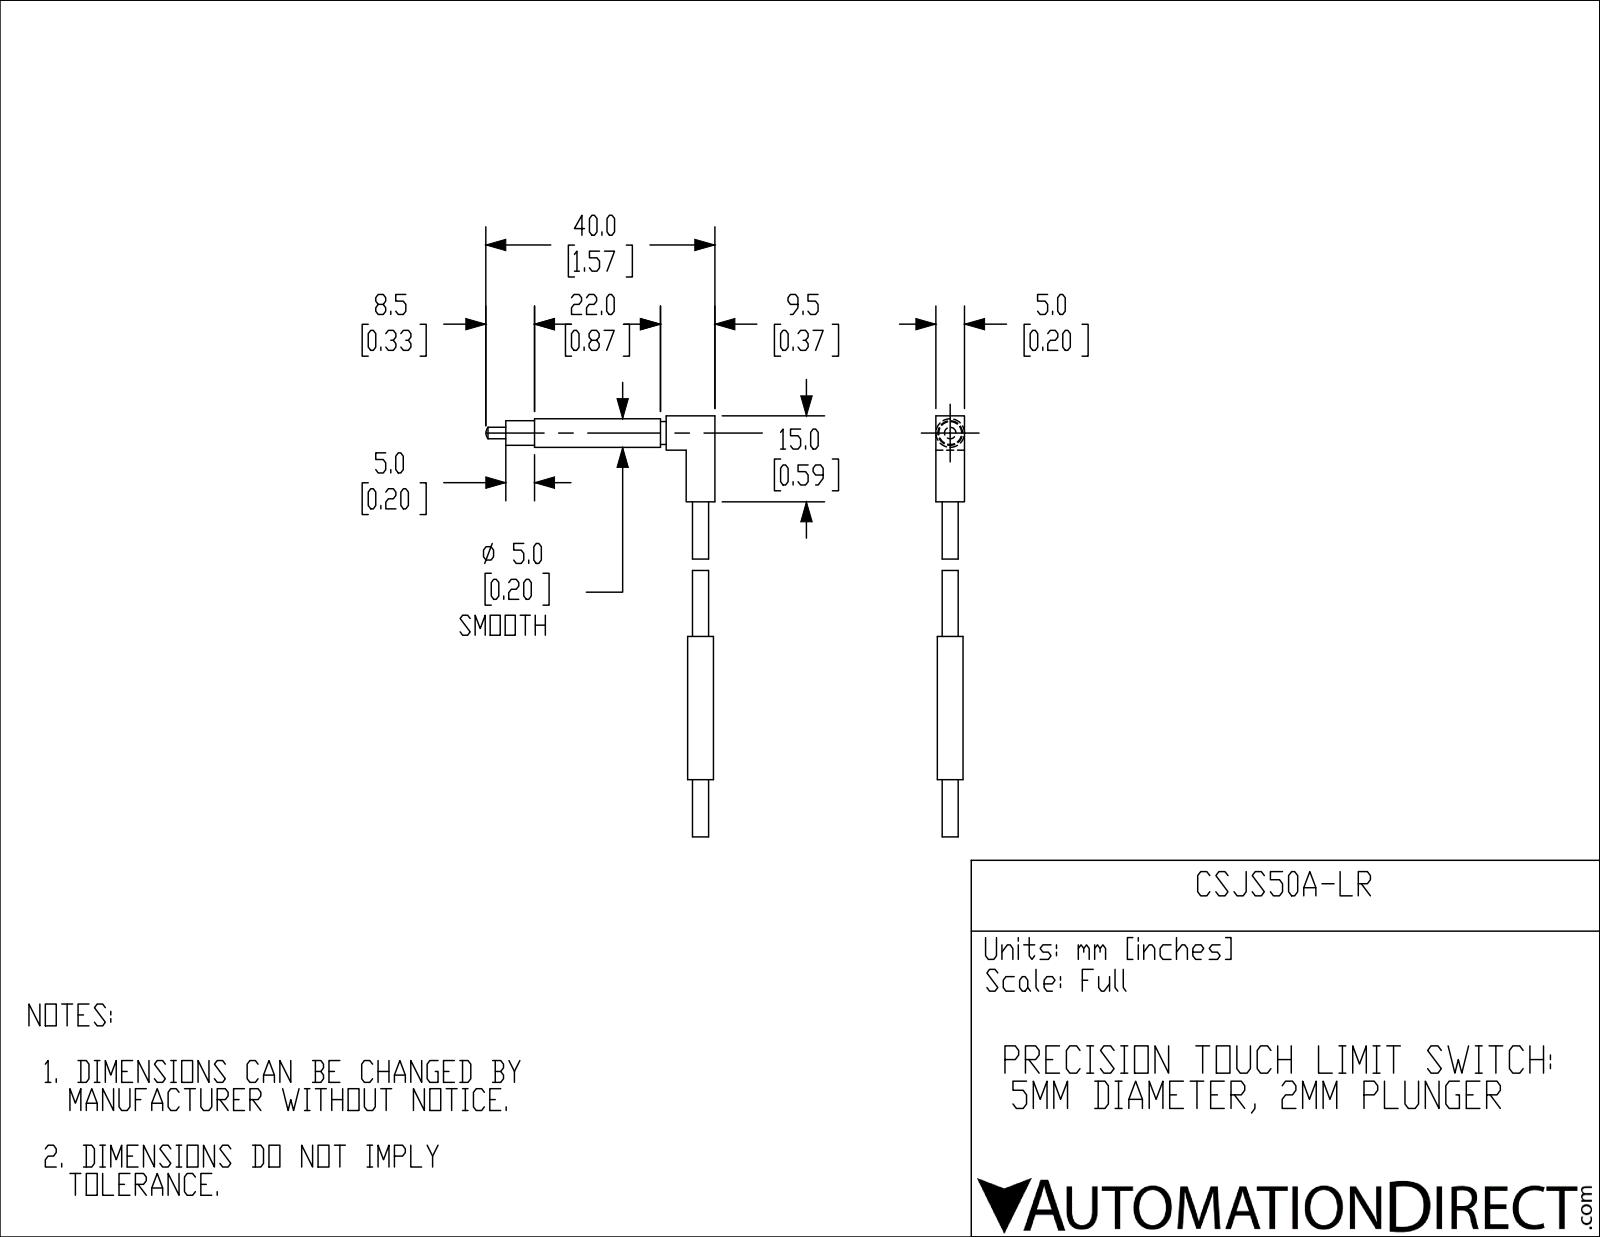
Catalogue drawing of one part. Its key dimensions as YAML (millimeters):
part_name: "CSJS50A-LR"
step_written_by: "SolidWorks 2018 (AUTOMOTIVE_DESIGN)"
units: millimeters
bodies: {solids: 2, faces: 25, planar: 16, cylindrical: 8, other: 1}
overall_size: [73.5, 40, 5]
volume: 1600
surface_area: 1549
round_bosses_or_shafts:
  - {diameter: 5, count: 1}
  - {diameter: 4.5, count: 1}
  - {diameter: 4.3, count: 1}
  - {diameter: 4, count: 1}
  - {diameter: 2.8, count: 1}
  - {diameter: 2, count: 1}
face_to_face_distances: [5, 15, 36.5, 9, 6, 3.5, 8.5, 31.5, 48.5, 25]
